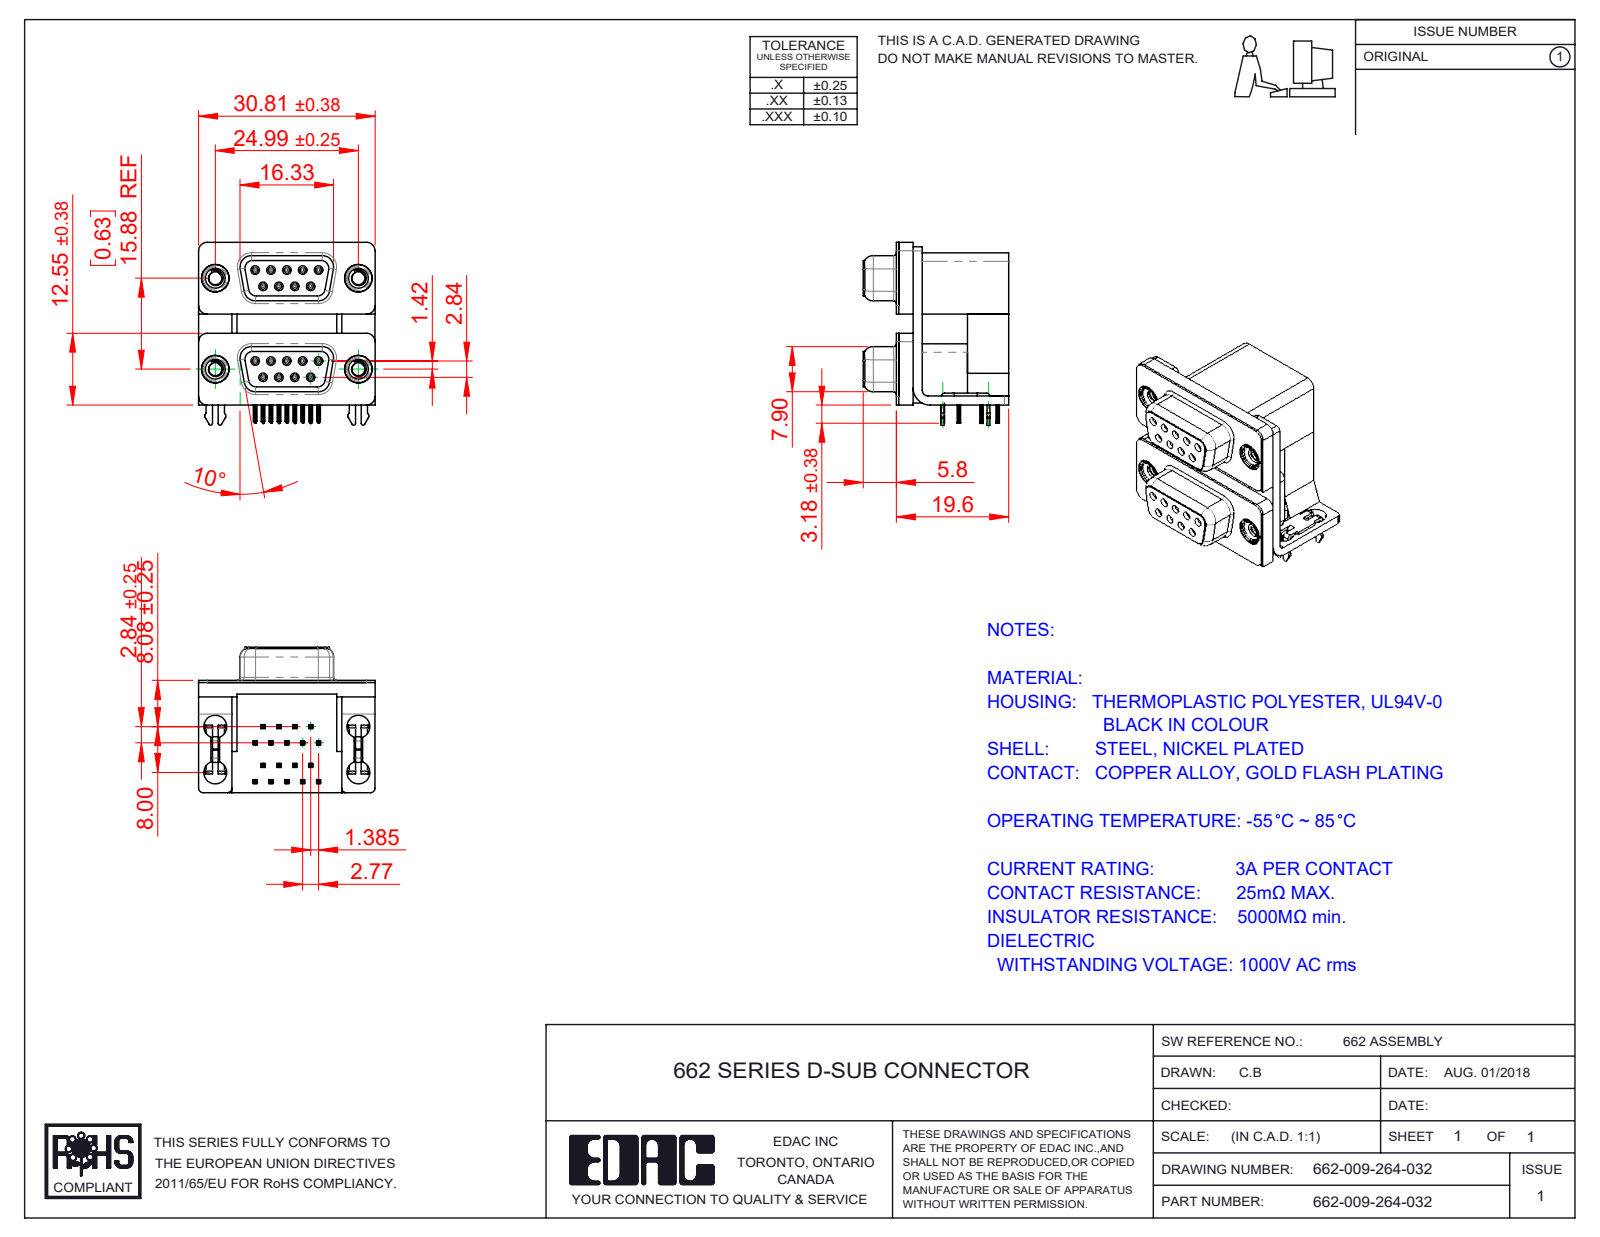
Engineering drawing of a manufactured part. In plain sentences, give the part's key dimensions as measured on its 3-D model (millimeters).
The part is named "662 Housing Spacer_09 Contacts L; 662 2 Prong Board Lock_3; 662 Contact Bottom Lower; 662 Shell_09 Contacts (+8 more)". Its 3-D file was written by "SolidWorks 2020 (CONFIG_CONTROL_DESIGN)". It is 31 solids with 3262 faces: 1476 planar, 846 cylindrical and 940 other. Overall it measures 31.93 by 30.81 by 25.4 millimeters. Its volume is 10 858 cubic millimeters and its surface area 13 044 square millimeters. Round holes: 18 of diameter 0.8, 18 of diameter 0.9, 8 of diameter 4, 4 of diameter 2.26, 4 of diameter 3.5, 4 of diameter 4.8, 4 of diameter 5. Round bosses or shafts: 18 of diameter 1.2, 4 of diameter 4.9, 4 of diameter 4.75, 4 of diameter 3.9. Partial cylindrical surfaces (rounded edges, fillets, slot ends): 146 of radius 0.1, 72 of radius 0.15, 36 of radius 0.35, 18 of radius 0.34, 18 of radius 1.35, 12 of radius 0.5, 12 of radius 1.5, 10 of radius 0.25. The main face-to-face distances are 2.5, 0.4, 16.7, 19.2, 2.9, 19.6, 15.88, 7.2, 9.5, 12. The hole center spacings are 3.16, 2.77, 16.12, 15.88, 5.54, 16.82, 13.11, 18.77.
